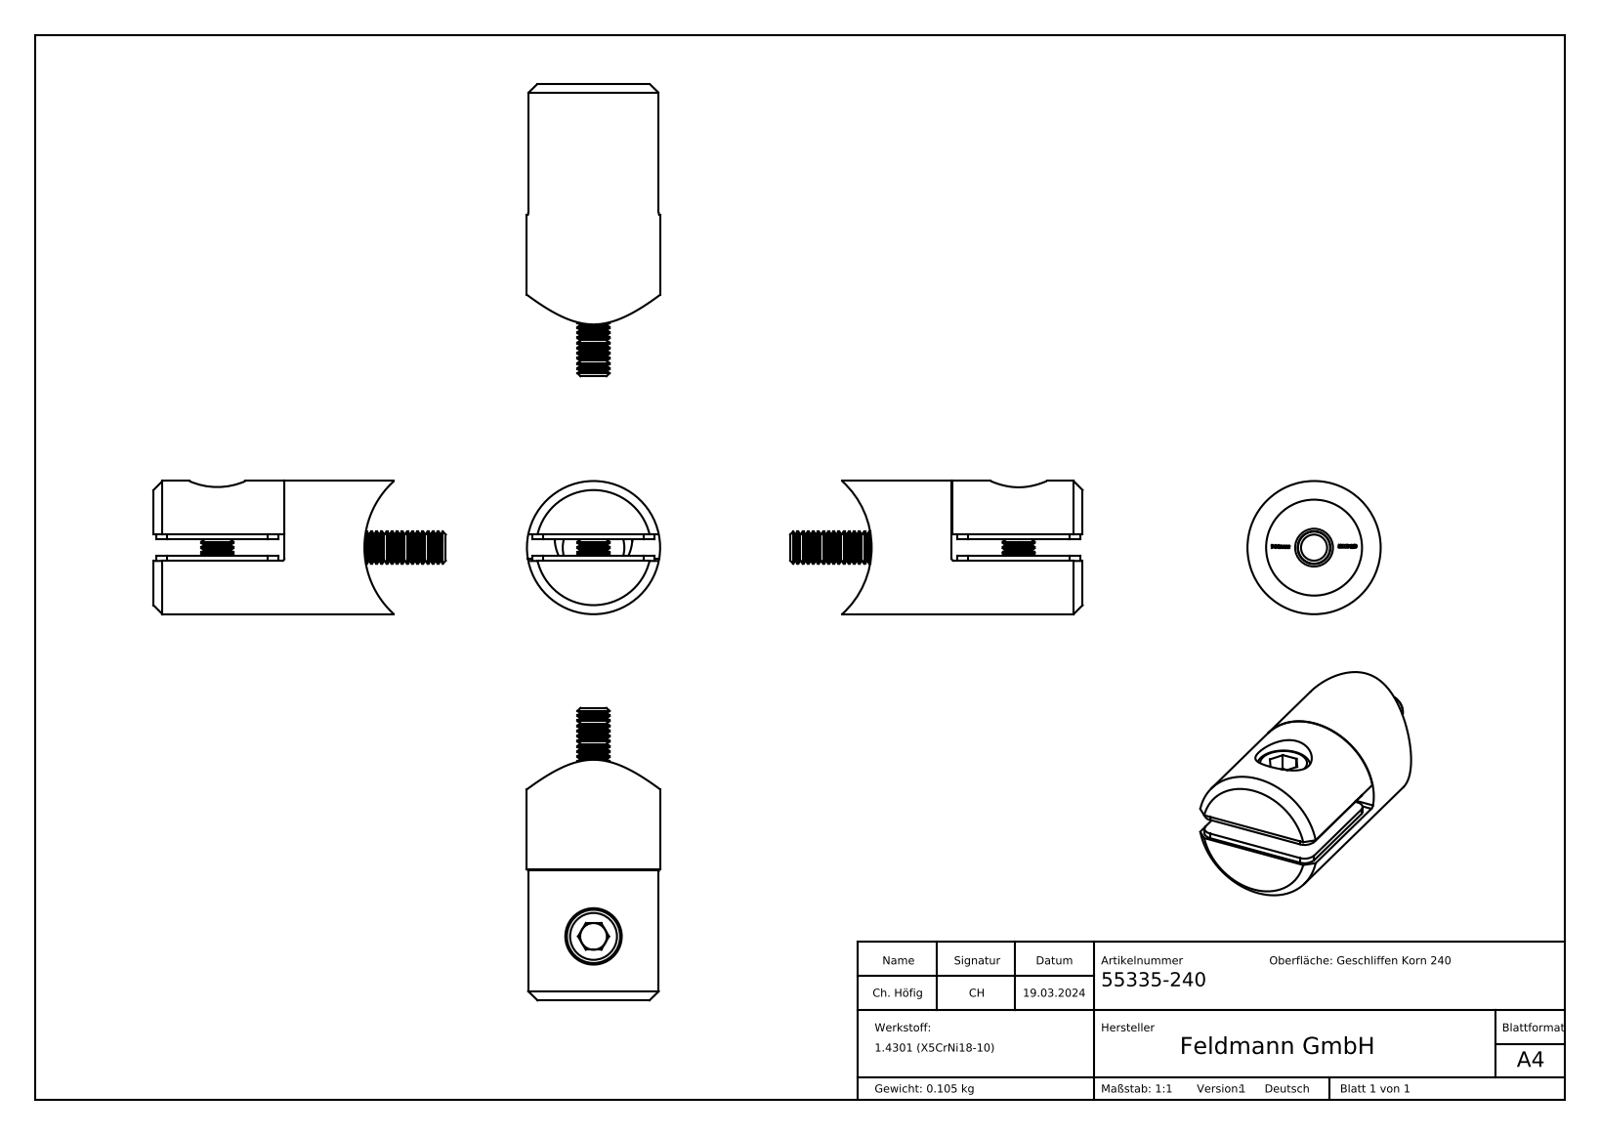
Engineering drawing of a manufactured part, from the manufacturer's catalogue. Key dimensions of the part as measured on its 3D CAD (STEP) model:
Part name (STEP PRODUCT): 5533X-240 Teil2_5533X-240 Teil2; 5533x-240 Teil3_5533x-240 Teil3; socket countersunk head screw_din_DIN 7991 - M6 x 25 --- 25S; 5533X-240 Teil1_55335-240 Teil1 (+2 more)
STEP written by: SolidWorks 2018 (CONFIG_CONTROL_DESIGN)
Units: millimetres
Bodies: 6 solids, 716 faces (215 planar, 187 cylindrical, 314 other)
Overall size (bounding box): 54.88 × 25 × 25
Volume: 15 522 mm³ · Surface area: 10 653 mm²
Round holes (diameter × count): ⌀4 ×2, ⌀5 ×1, ⌀6.5 ×1, ⌀7 ×1, ⌀7.1 ×1, ⌀10.58 ×1, ⌀14.6 ×1, ⌀18 ×1
Round bosses / shafts (diameter × count): ⌀6 ×2, ⌀25 ×1, ⌀11.57 ×1, ⌀10 ×1
Partial cylindrical surfaces — rounded edges, fillets, slot ends (radius × count): R0.2 ×40, R2 ×6, R1.25 ×2, R0.5 ×1, R16.85 ×1
Main face-to-face distances: 4, 1, 5, 3, 10, 34.5, 24.5, 6, 9.9, 24.6
Hole centre spacings: 9.37, 12
